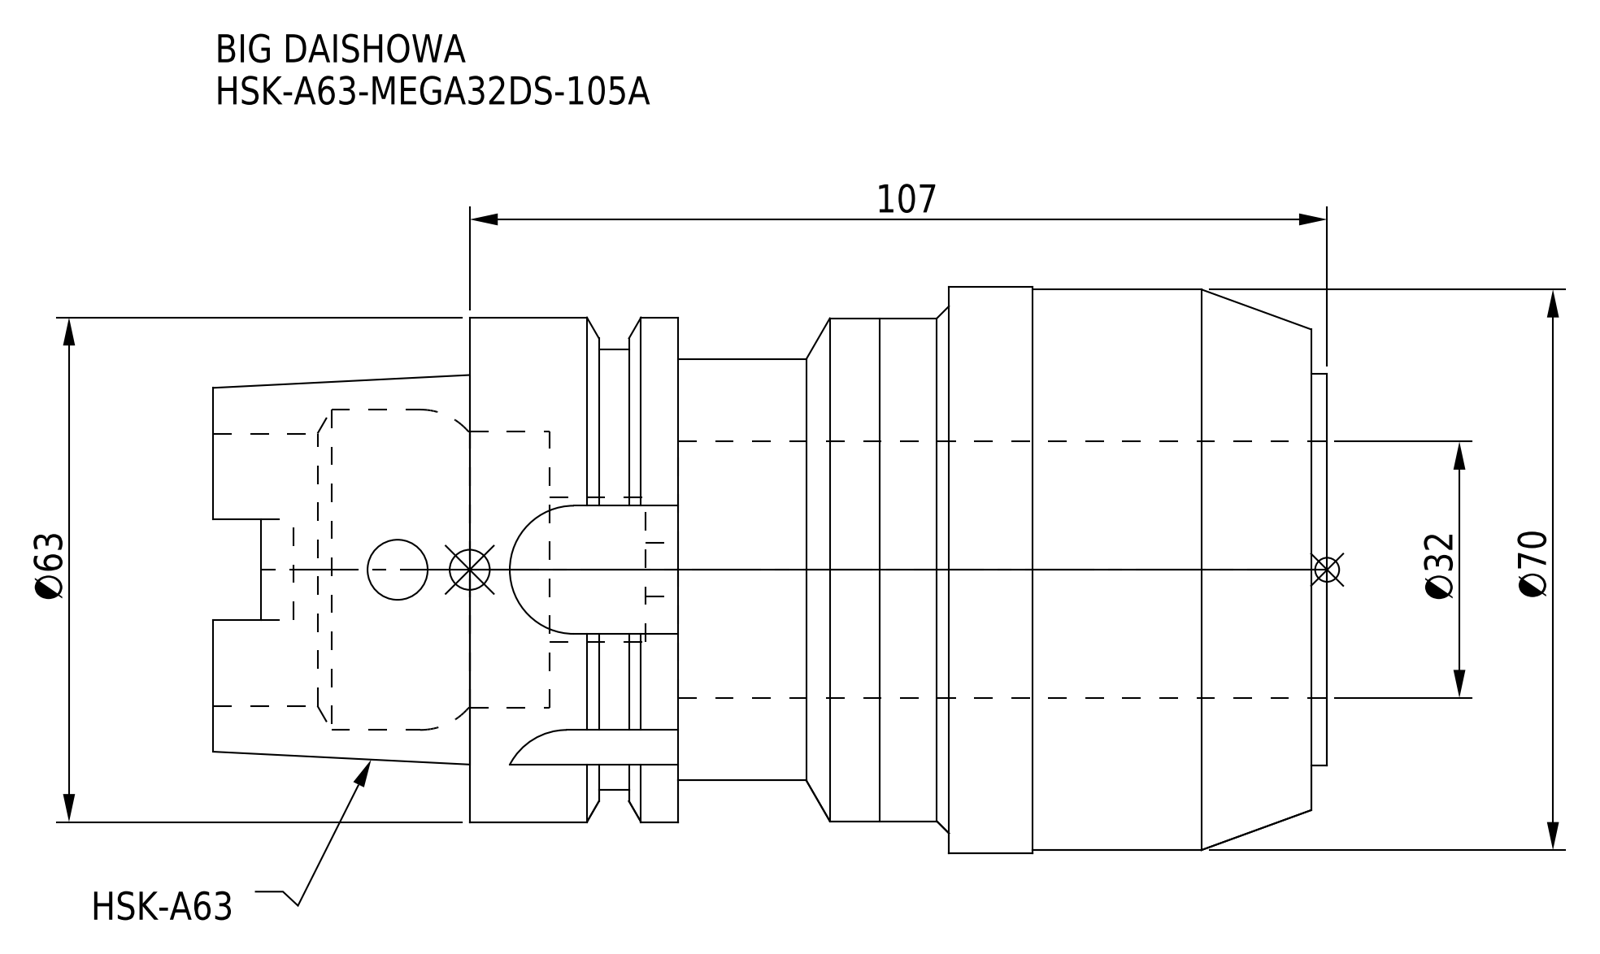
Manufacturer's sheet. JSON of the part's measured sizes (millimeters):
{"part_name": "HSK-A63-MEGA32DS-105A", "step_written_by": "CREO PARAMETRIC BY PTC INC, 2016380 (AUTOMOTIVE_DESIGN)", "units": "millimeters", "bodies": {"solids": 1, "faces": 103, "planar": 40, "cylindrical": 43, "other": 20}, "overall_size": [139, 70.7, 70.7], "volume_mm3": 276618, "surface_area_mm2": 48743, "round_holes": [[6.75, 1], [7.5, 1], [18, 1], [32, 1], [34, 1], [34.5, 1], [40, 1]], "round_bosses_or_shafts": [[70.7, 1], [70, 1], [63, 1], [62.8, 1], [55, 1], [52.6, 1], [48.9, 1]], "partial_cylinders_radius": [[2.88, 4], [8, 4]], "face_to_face_distances": [26, 81, 107, 2, 79, 105, 97.05, 95.05, 16.05, 9.95]}
